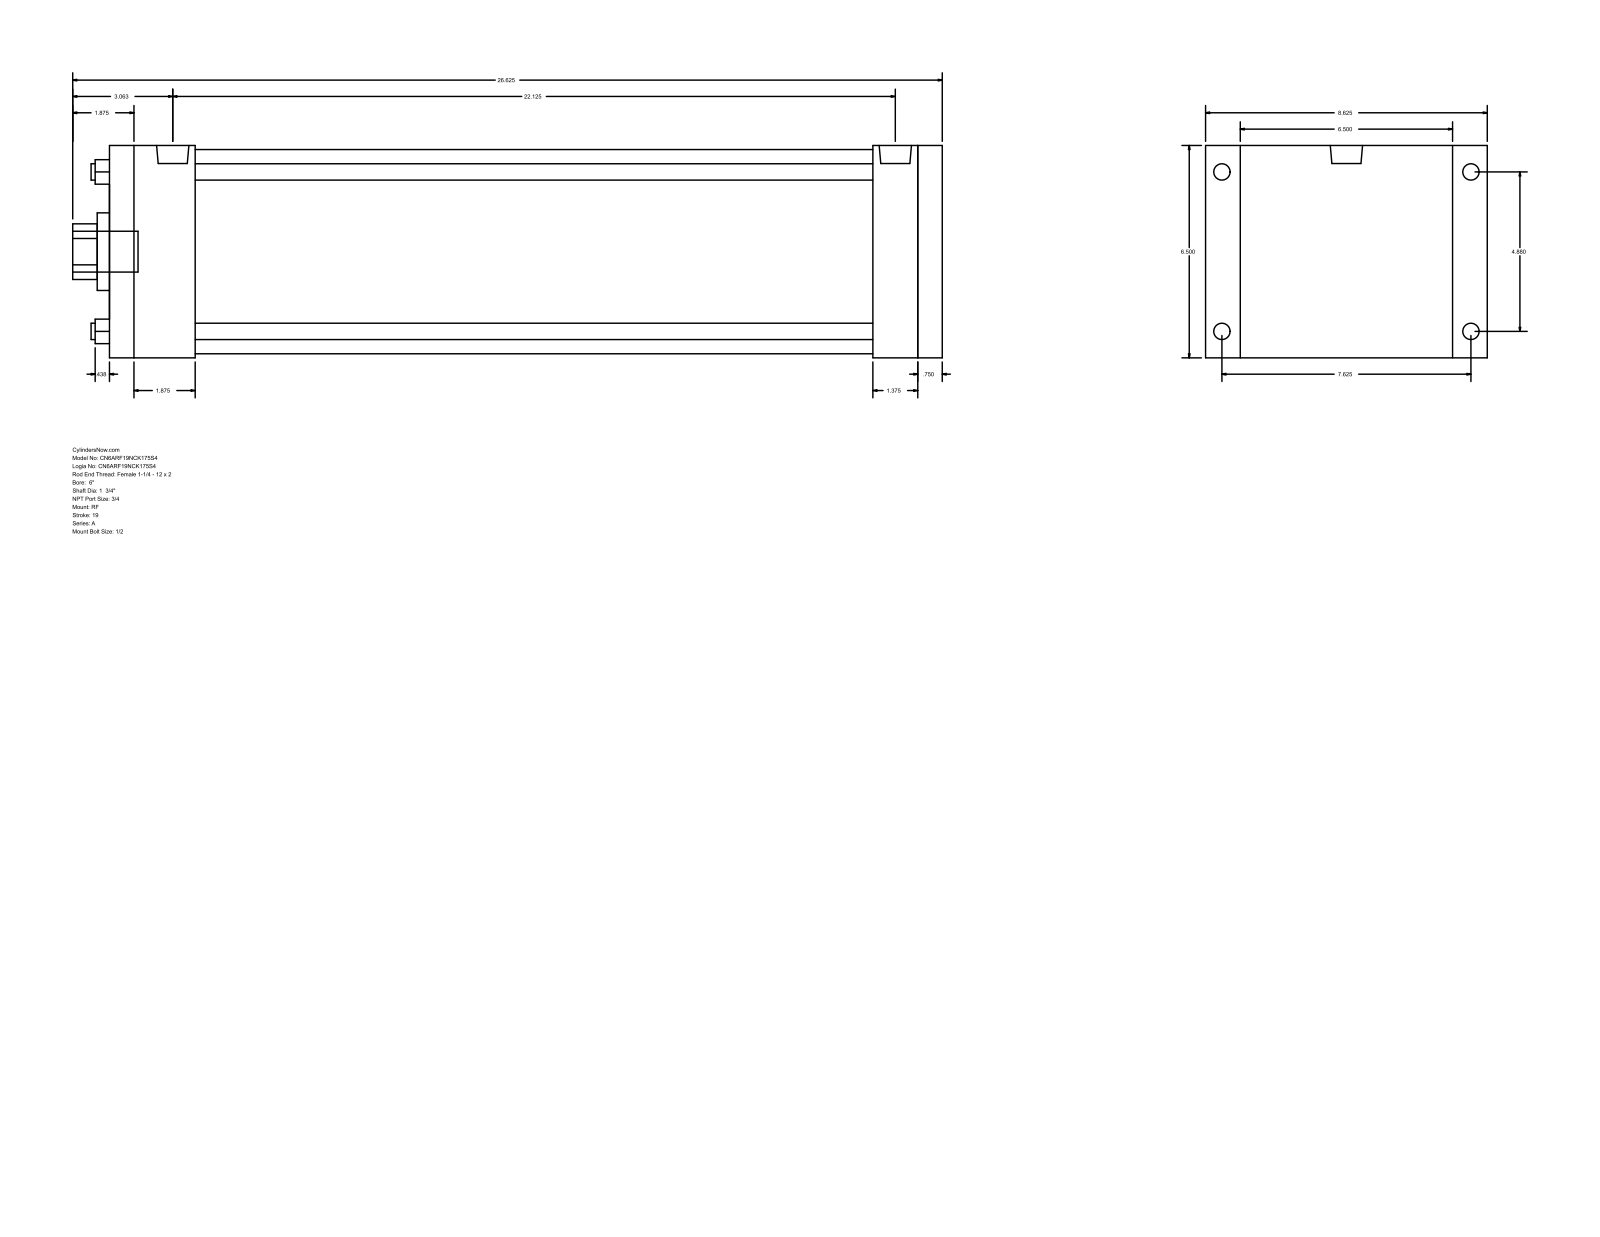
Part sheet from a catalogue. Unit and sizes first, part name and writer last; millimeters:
Units: millimetres
Overall size (bounding box): 676.27 × 219.07 × 165.1
Round holes (diameter × count): ⌀12.7 ×4, ⌀44.45 ×1, ⌀60.33 ×1, ⌀158.75 ×1
Round bosses / shafts (diameter × count): ⌀15.08 ×4, ⌀12.7 ×4, ⌀25.12 ×2, ⌀31.75 ×1
Partial cylindrical surfaces — rounded edges, fillets, slot ends (radius × count): R21.63 ×1
Main face-to-face distances: 165.1, 647.7, 628.66, 19.04, 66.68, 561.98, 581.02, 593.73, 527.05, 34.93
Hole centre spacings: 87.65, 123.96, 175.31
Bodies: 0 solids, 92 faces (64 planar, 28 cylindrical, 0 other)
Part name (STEP PRODUCT): A_RF__0600_1.75
STEP written by: GSSL Pune (CONFIG_CONTROL_DESIGN)
